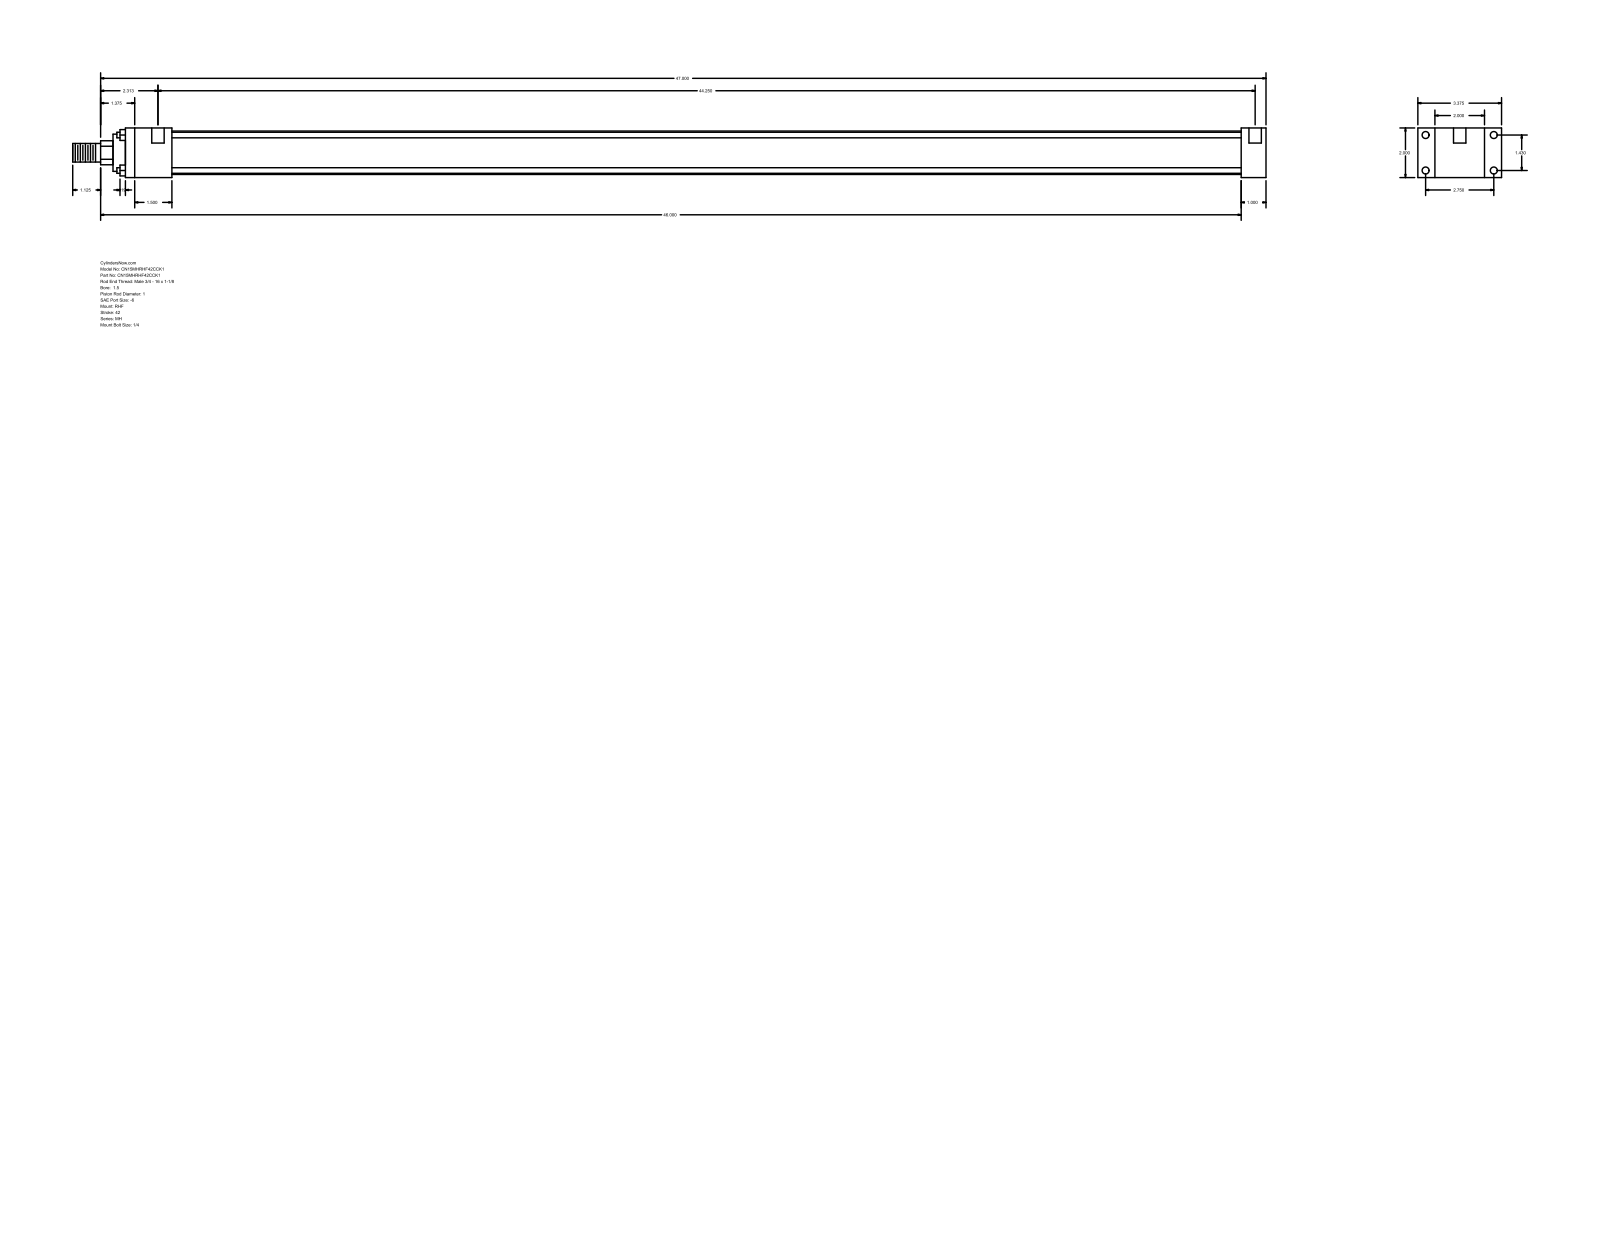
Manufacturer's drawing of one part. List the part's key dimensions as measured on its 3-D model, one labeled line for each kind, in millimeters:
Part name (STEP PRODUCT): MH_RHF__0150_1
STEP written by: GSSL Pune (CONFIG_CONTROL_DESIGN)
Units: millimetres
Bodies: 0 solids, 88 faces (60 planar, 28 cylindrical, 0 other)
Overall size (bounding box): 1222.38 × 85.72 × 50.8
Round holes (diameter × count): ⌀5.56 ×4, ⌀7.14 ×4, ⌀12.7 ×2
Round bosses / shafts (diameter × count): ⌀5.71 ×4, ⌀44.45 ×1, ⌀38.1 ×1, ⌀25.4 ×1, ⌀19.05 ×1
Partial cylindrical surfaces — rounded edges, fillets, slot ends (radius × count): R12.29 ×1
Main face-to-face distances: 50.8, 25.4, 17.46, 68.26, 85.72, 1168.4, 1143, 47.63, 1095.37, 1120.77
Hole centre spacings: 36.32, 69.84, 78.72, 1127.13, 3.18, 1123.95
